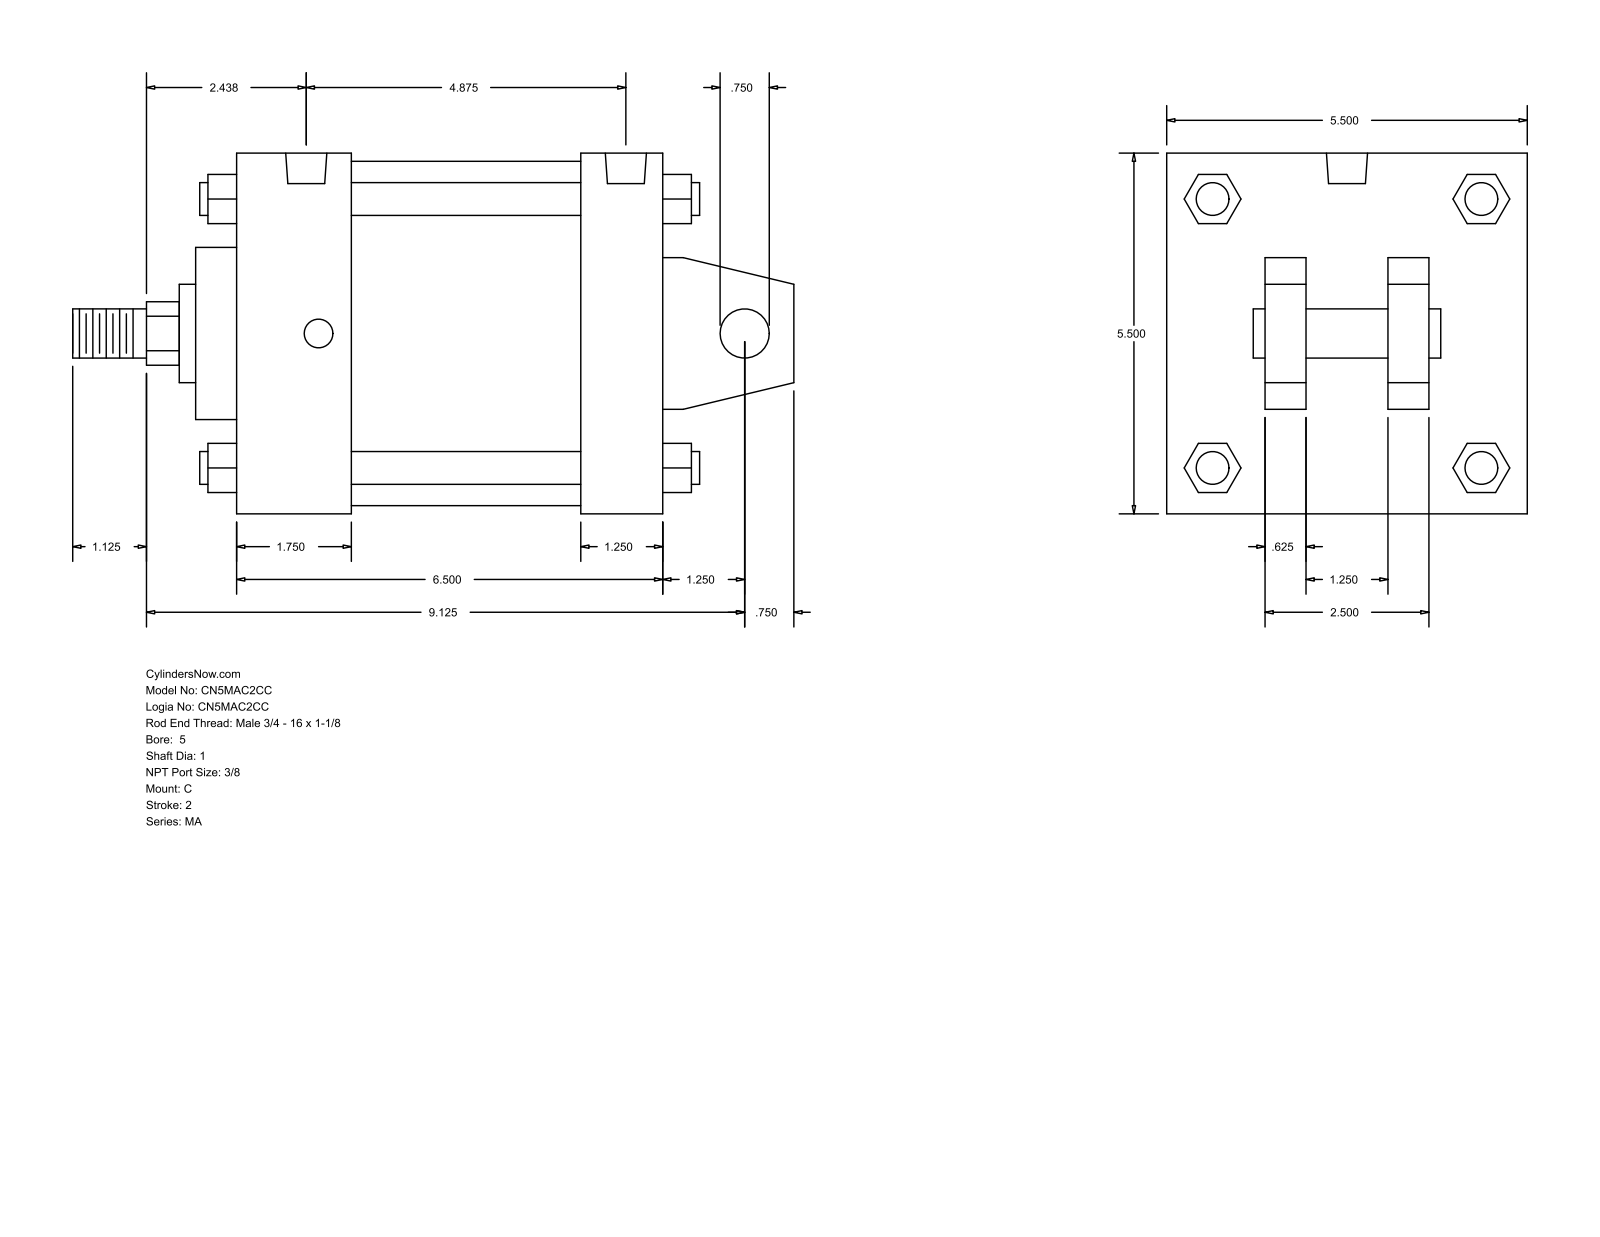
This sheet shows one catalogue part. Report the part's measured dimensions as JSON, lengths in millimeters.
{"part_name": "MA_C__0500_1", "step_written_by": "GSSL Pune (CONFIG_CONTROL_DESIGN)", "units": "millimeters", "bodies": {"solids": 0, "faces": 141, "planar": 109, "cylindrical": 32, "other": 0}, "overall_size": [279.4, 139.7, 139.7], "round_holes": [[11.11, 4], [15.93, 2]], "round_bosses_or_shafts": [[12.7, 4], [19.05, 2], [133.35, 1], [66.67, 1], [38.1, 1], [25.4, 1]], "partial_cylinders_radius": [[12.29, 1]], "face_to_face_distances": [139.7, 165.11, 15.87, 133.36, 31.75, 44.46, 88.9, 120.65, 38.1, 101.6], "hole_center_spacings": [114.3, 4.76, 4.77, 119.06, 119.07, 123.83]}
